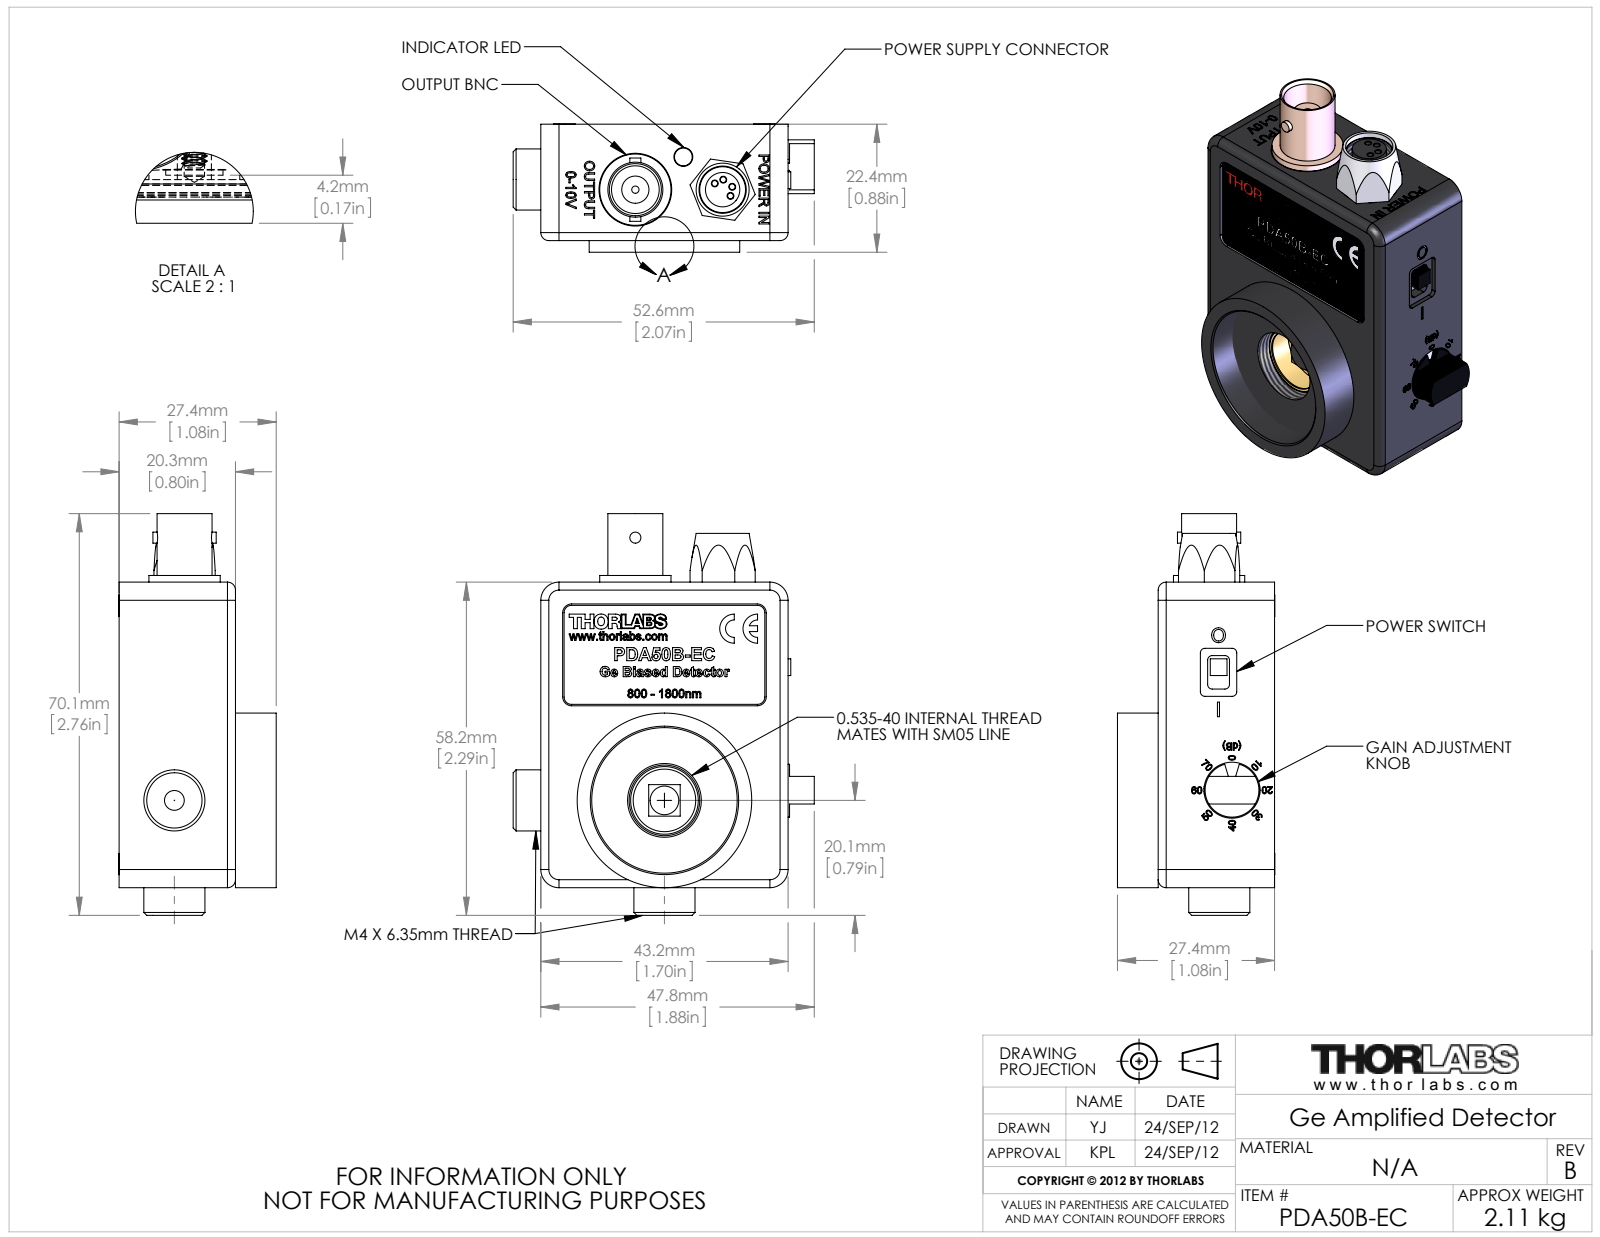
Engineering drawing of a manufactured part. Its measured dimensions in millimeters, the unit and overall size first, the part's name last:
Units: millimetres
Overall size (bounding box): 70.12 × 52.58 × 27.47
Round holes (diameter × count): ⌀0.94 ×9, ⌀0.81 ×8, ⌀1.78 ×7, ⌀2.44 ×6, ⌀0.2 ×5, ⌀0.76 ×4, ⌀1 ×4, ⌀3.17 ×4, ⌀5.08 ×4, ⌀1.27 ×3, ⌀3.45 ×2, ⌀3.81 ×2
Round bosses / shafts (diameter × count): ⌀3.73 ×4, ⌀2.18 ×4, ⌀10.67 ×2, ⌀9.4 ×2, ⌀5.99 ×2, ⌀0.45 ×2, ⌀30.48 ×1, ⌀26.29 ×1
Partial cylindrical surfaces — rounded edges, fillets, slot ends (radius × count): R0.2 ×46, R0.1 ×36, R3.17 ×23, R0.25 ×10, R0.35 ×8, R0.79 ×8, R2.41 ×8, R1.27 ×5
Main face-to-face distances: 1.59, 2.54, 12.76, 14.35, 1.58, 12.77, 1.78, 11.18, 1.27, 0.51
Hole centre spacings: 2.54, 2, 3.2, 3.25, 3.59, 5.08, 5.15, 7.11
Volume: 24 613 mm³ · Surface area: 28 569 mm²
Bodies: 56 solids, 4225 faces (2458 planar, 861 cylindrical, 906 other)
Part name (STEP PRODUCT): 14031-E0W
STEP written by: SolidWorks 2011 (AUTOMOTIVE_DESIGN)
